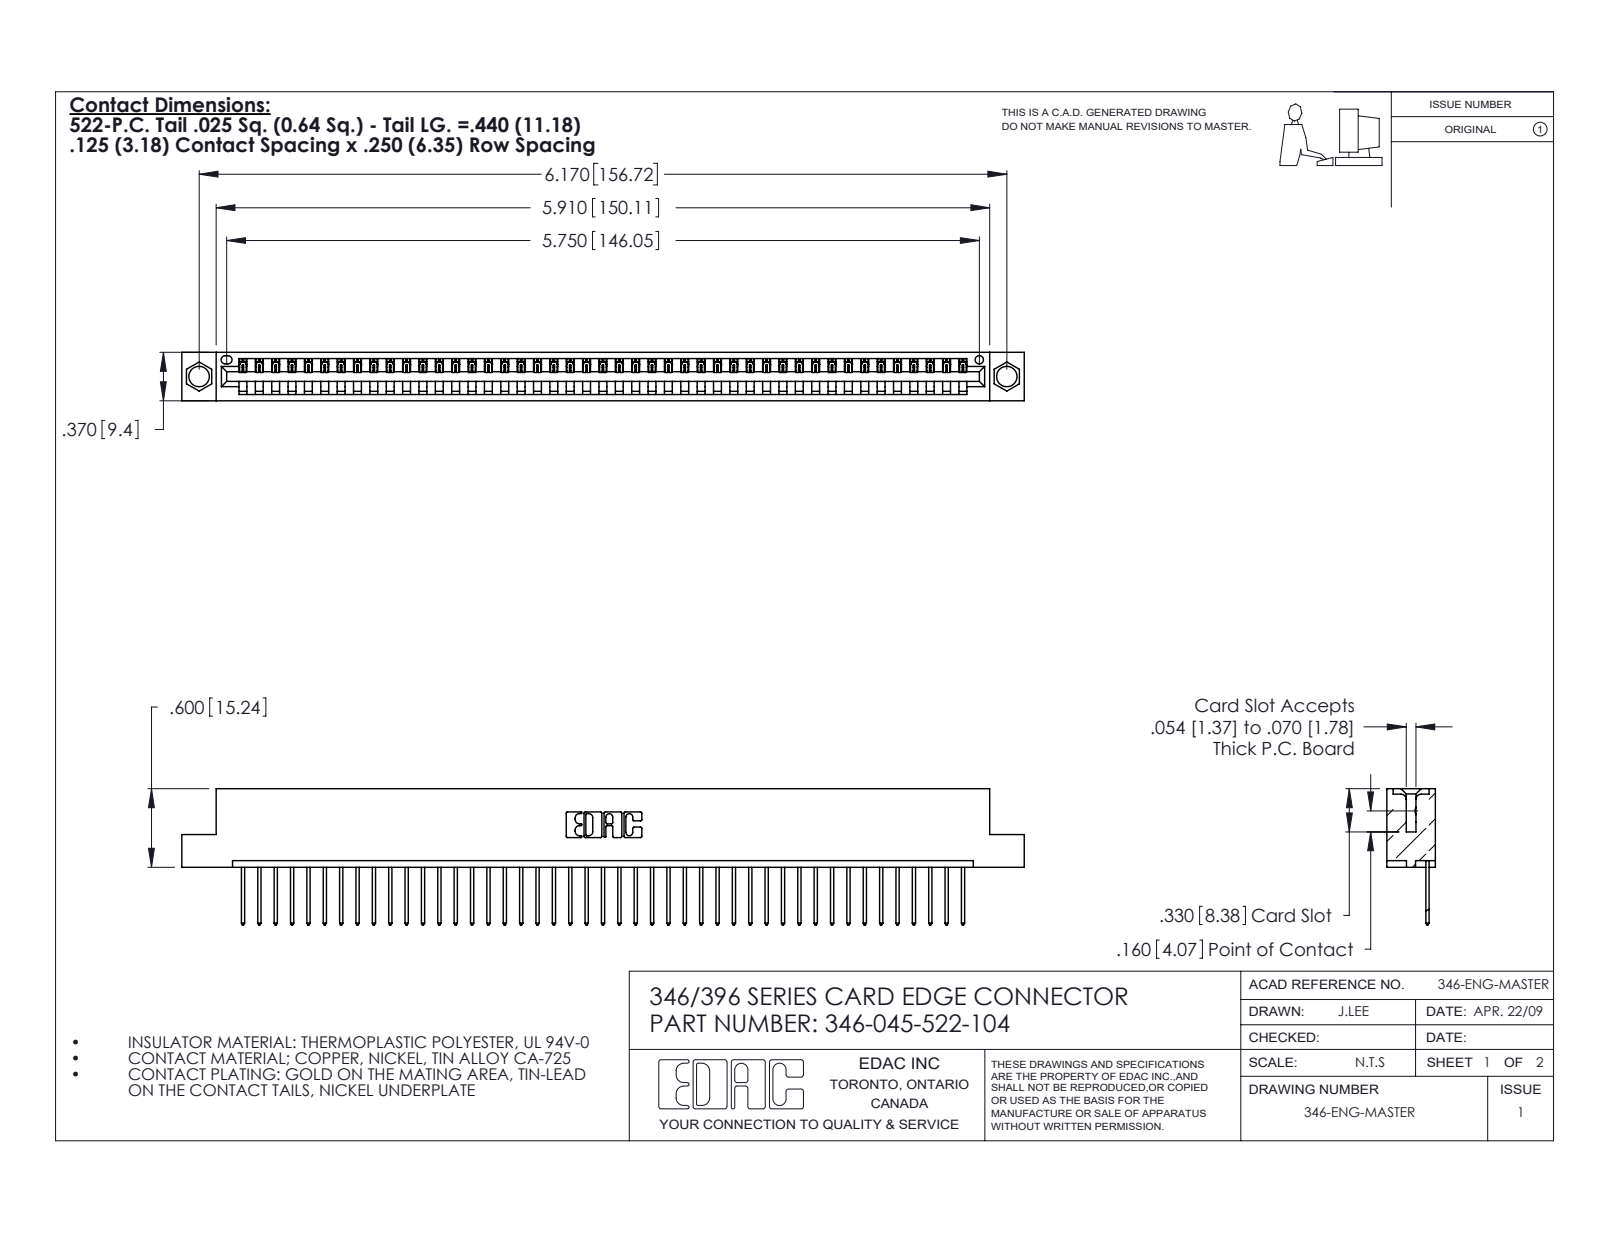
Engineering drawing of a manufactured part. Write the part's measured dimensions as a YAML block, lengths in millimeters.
part_name: "345-292-001_345-293-122; 346 Part_Flush Mounting Lugs - 0.156 Dia-TH; 346-045-522-104"
step_written_by: "SolidWorks 2020 (CONFIG_CONTROL_DESIGN)"
units: millimeters
bodies: {solids: 46, faces: 2746, planar: 1890, cylindrical: 856, other: 0}
overall_size: [163.4, 26.4, 9.4]
volume: 15600
surface_area: 19490
round_holes:
  - {diameter: 4, count: 2}
  - {diameter: 1.6, count: 1}
partial_cylinders:
  - {radius: 0.2, count: 90}
  - {radius: 0.3, count: 90}
  - {radius: 0.3, count: 22}
  - {radius: 0.2, count: 6}
  - {radius: 0.8, count: 6}
  - {radius: 0.7, count: 3}
  - {radius: 0.8, count: 2}
  - {radius: 1, count: 2}
face_to_face_distances: [1.2, 8.2, 9.4, 6.4, 1.8, 7.6, 0.6, 3.8, 5.6, 2.5]
hole_center_spacings: [6.2, 151.4, 156.7]
